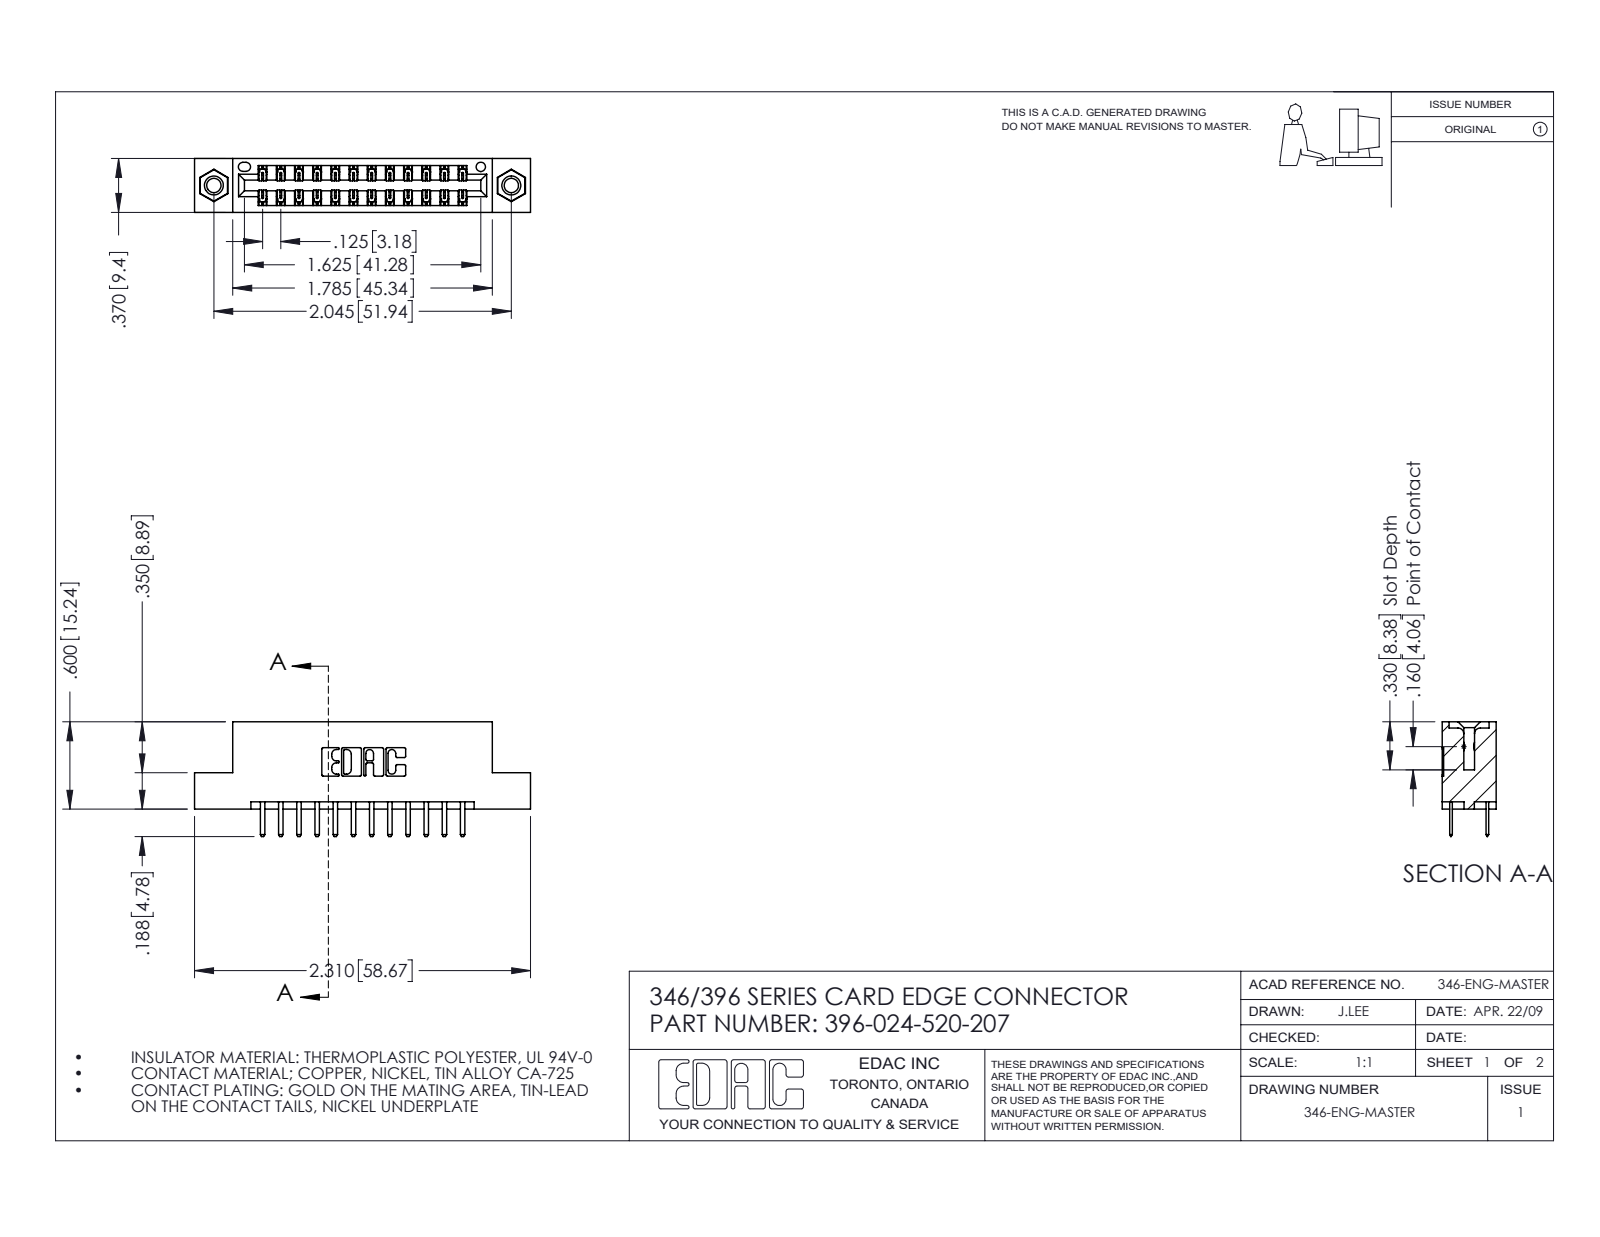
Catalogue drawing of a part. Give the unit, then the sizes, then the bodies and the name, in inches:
Units: inches
Overall size (bounding box): 2.31 × 0.788 × 0.37
Round holes (diameter × count): ⌀0.098 ×2, ⌀0.125 ×2, ⌀0.156 ×2, ⌀0.064 ×1
Round bosses / shafts (diameter × count): ⌀0.155 ×2
Partial cylindrical surfaces — rounded edges, fillets, slot ends (radius × count): R0.006 ×36, R0.01 ×28, R0.01 ×22, R0.007 ×6, R0.031 ×6, R0.026 ×3, R0.014 ×2, R0.022 ×2
Main face-to-face distances: 0.25, 0.048, 0.322, 0.37, 0.275, 0.148, 0.222, 0.1, 0.174, 0.072
Hole centre spacings: 0.246, 1.839, 2.045
Volume: 0.333 in³ · Surface area: 10.93 in²
Bodies: 27 solids, 1526 faces (996 planar, 514 cylindrical, 16 other)
Part name (STEP PRODUCT): 346 Part_Flush Mounting Lugs - 0.156 Dia-TI; 396-024-520-207; 345-250-001_345-250-005-103; 345-292-001_345-293-120
STEP written by: SolidWorks 2016 (CONFIG_CONTROL_DESIGN)
